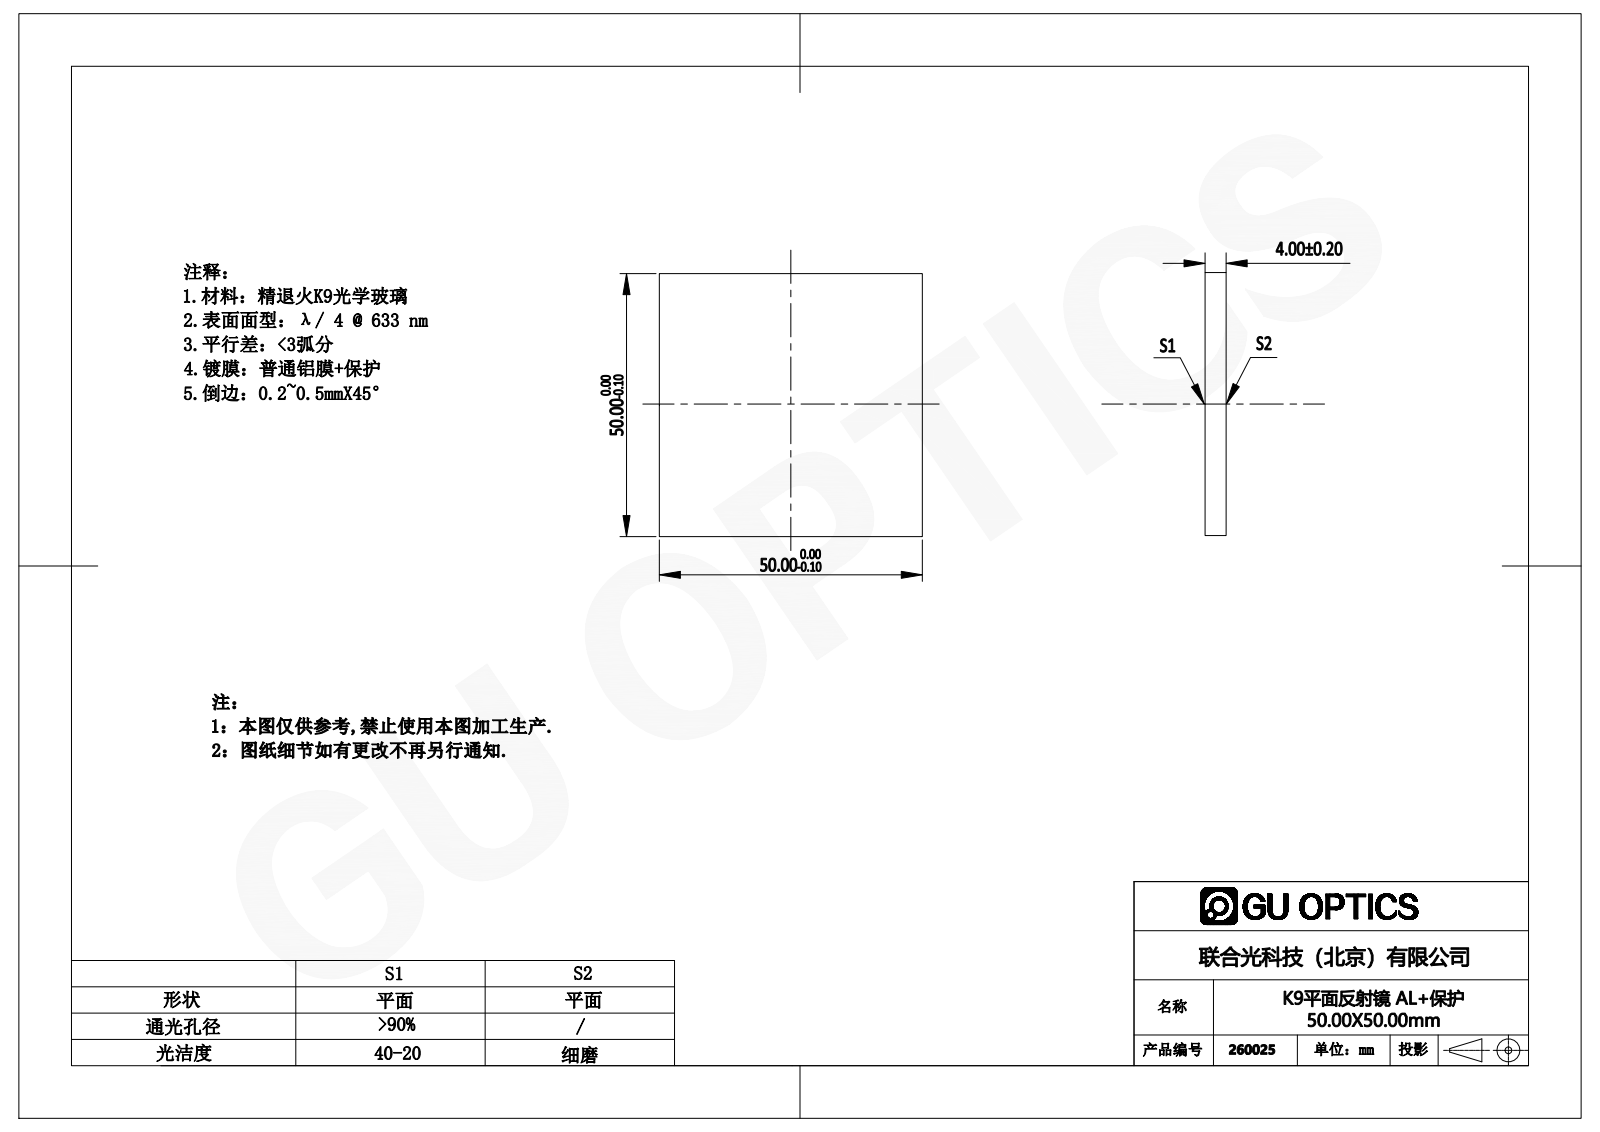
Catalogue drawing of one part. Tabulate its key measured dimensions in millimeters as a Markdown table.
| quantity | value |
| --- | --- |
| part name | 260012 |
| STEP written by | SolidWorks 2016 (AUTOMOTIVE_DESIGN) |
| units | millimeters |
| bodies | 1 solid, 6 faces (6 planar, 0 cylindrical, 0 other) |
| overall size | 50 × 50 × 4 |
| volume | 10 000 mm³ |
| surface area | 5 800 mm² |
| main face-to-face distances | 4, 50 |
